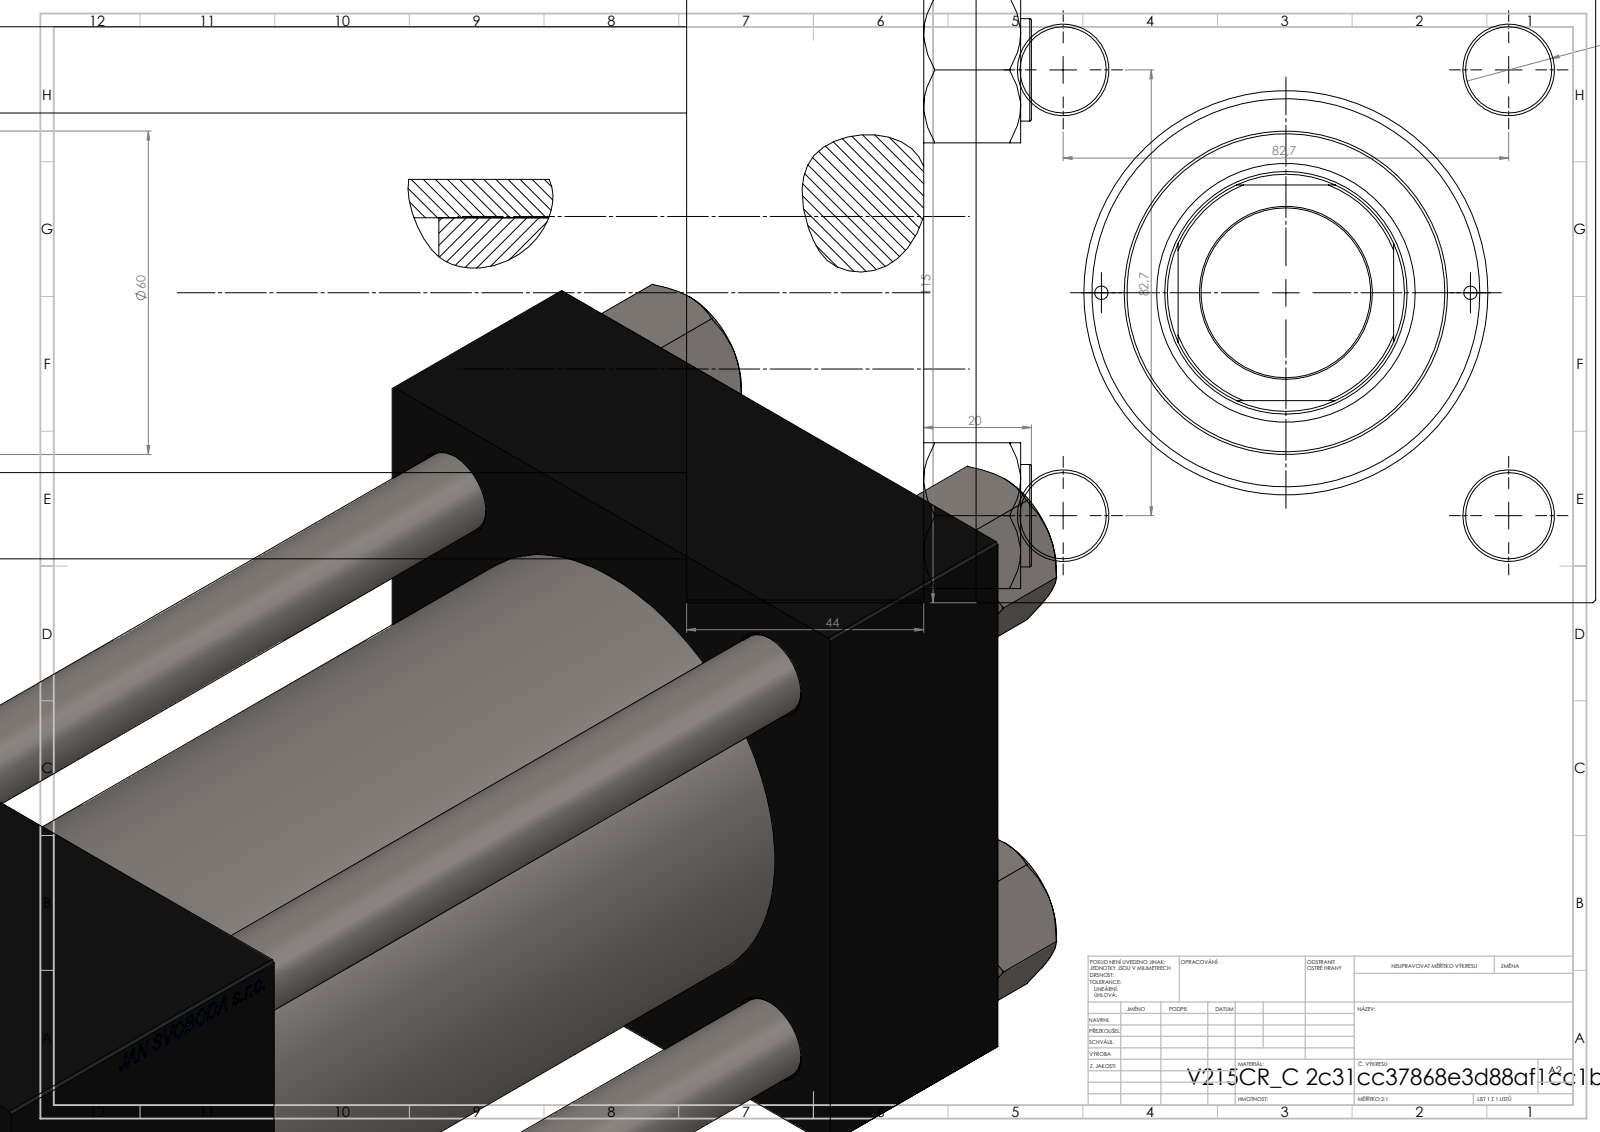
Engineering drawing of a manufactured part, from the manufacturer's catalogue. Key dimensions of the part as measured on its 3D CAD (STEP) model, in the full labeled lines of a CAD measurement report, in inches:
Part name (STEP PRODUCT): NUT_M5_C; V215_VC_A; V215CR_C_Body; V215CR_C_TYCINKA (+1 more)
STEP written by: SolidWorks 2019 (CONFIG_CONTROL_DESIGN)
Units: inches
Bodies: 11 solids, 1202 faces (576 planar, 90 cylindrical, 536 other)
Overall size (bounding box): 12.205 × 4.528 × 4.528
Volume: 126.6 in³ · Surface area: 531.8 in²
Round holes (diameter × count): ⌀0.63 ×4, ⌀0.098 ×2, ⌀0.276 ×2, ⌀1.041 ×2, ⌀1.378 ×2, ⌀1.24 ×1, ⌀1.772 ×1, ⌀1.89 ×1, ⌀2.402 ×1, ⌀2.835 ×1, ⌀3.15 ×1
Round bosses / shafts (diameter × count): ⌀0.748 ×4, ⌀3.386 ×1, ⌀2.362 ×1
Partial cylindrical surfaces — rounded edges, fillets, slot ends (radius × count): R0.866 ×1
Main face-to-face distances: 4.528, 1.732, 10.197, 8.465, 7.48, 5.748, 2.717, 3.937, 9.067, 7.335
Hole centre spacings: 1.652, 2.302, 3.256, 3.393, 1.348, 4.605, 2.697, 7.52
